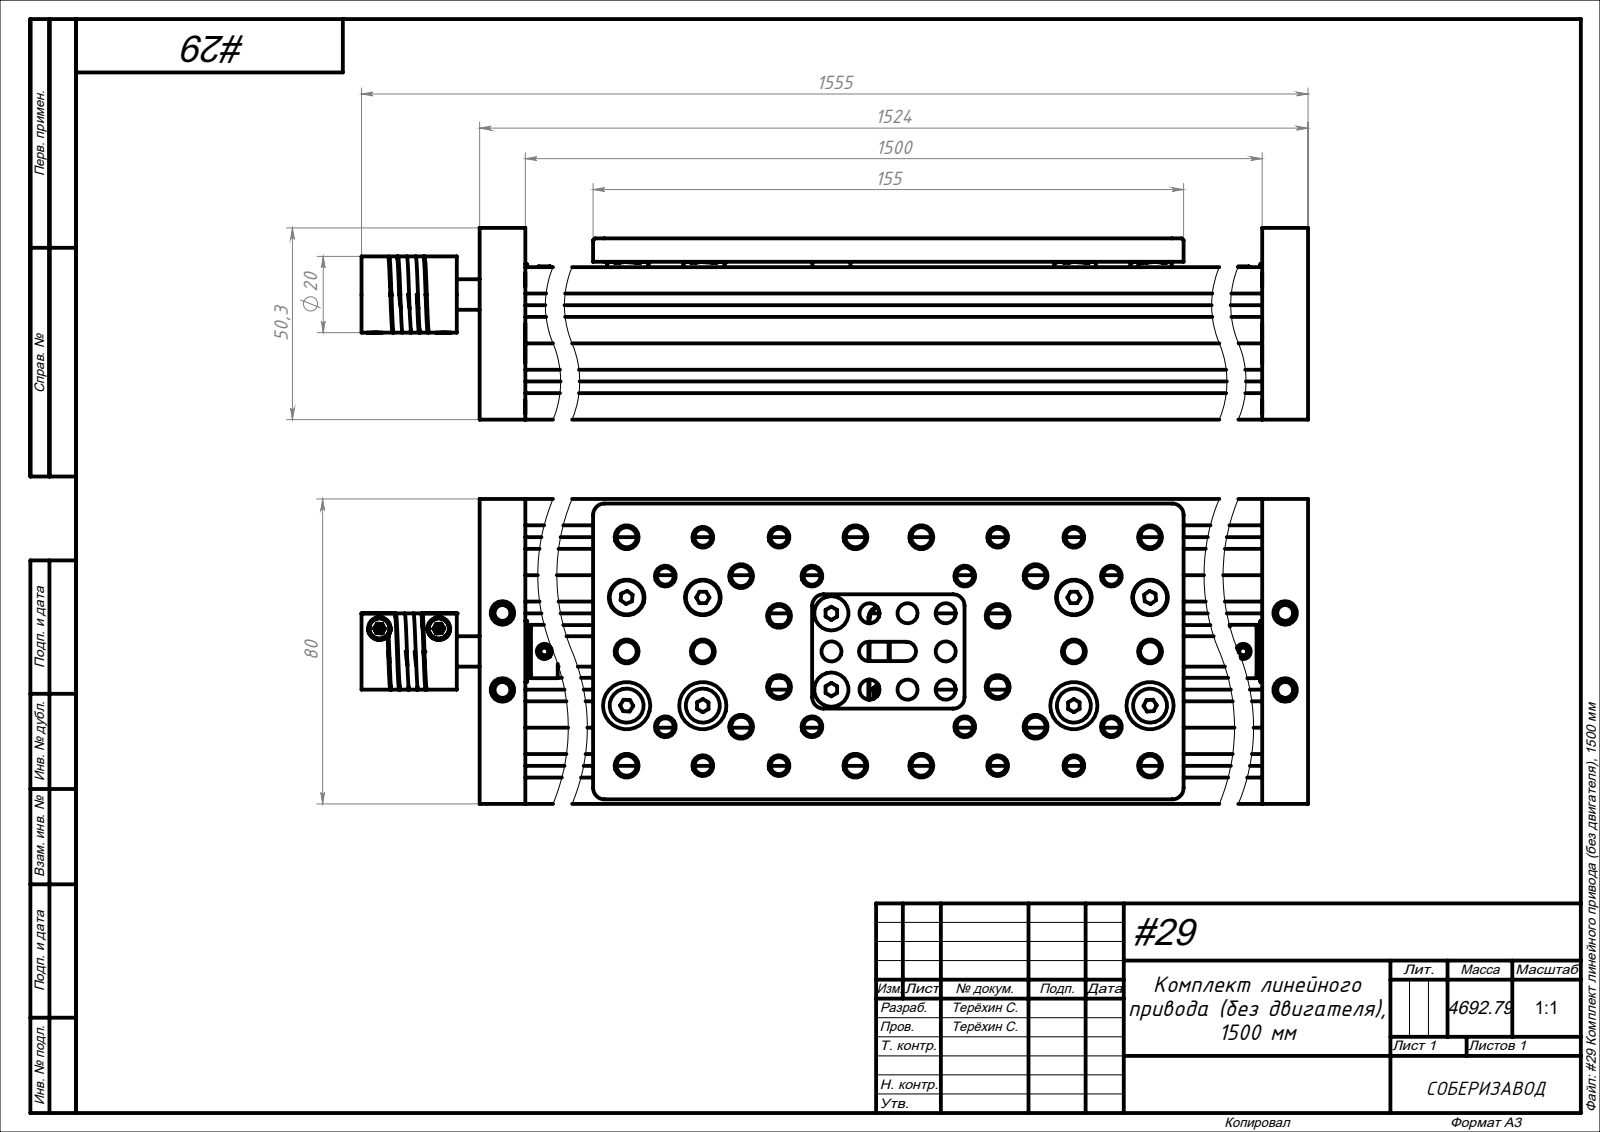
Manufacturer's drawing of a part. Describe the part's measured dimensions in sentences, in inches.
The part is named "A233 Ходовая гайка безлюфтовая 33x34_00; A371 Втулка резьбовая M7xM5_00; A182 Подшипник для трапецеидального винта, O 8 O 16, 688zz; Для муфты M4_M5(16) (+8 more)". Its 3-D file was written by "SolidWorks 2021 (AUTOMOTIVE_DESIGN)". It is 171 solids with 4603 faces: 1282 planar, 1432 cylindrical and 1889 other. Overall it measures 61.22 by 3.15 by 1.98 inches. Its volume is 98.31 cubic inches and its surface area 2 094 square inches. Round holes: 42 of diameter 0.209, 16 of diameter 0.177, 16 of diameter 0.197, 11 of diameter 0.165, 10 of diameter 0.163, 10 of diameter 0.203, 8 of diameter 0.24, 8 of diameter 0.307, 8 of diameter 0.331, 8 of diameter 0.341, 4 of diameter 0.205, 4 of diameter 0.283. Round bosses or shafts: 12 of diameter 0.315, 10 of diameter 0.308, 8 of diameter 0.6, 8 of diameter 0.352, 8 of diameter 0.34, 8 of diameter 0.276, 8 of diameter 0.247, 8 of diameter 0.236. Partial cylindrical surfaces (rounded edges, fillets, slot ends): 100 of radius 0.01, 86 of radius 0.008, 48 of radius 0.079, 40 of radius 0.039, 30 of radius 0.012, 20 of radius 0.055, 8 of radius 0.118, 6 of radius 0.059. The main face-to-face distances are 0.557, 1.113, 0.787, 0.071, 0.486, 0.472, 0.236, 0.551, 1.67, 0.111. The hole center spacings are 0.787, 0.394, 0.881, 2.122, 0.588, 0.614, 0.704, 0.789.
